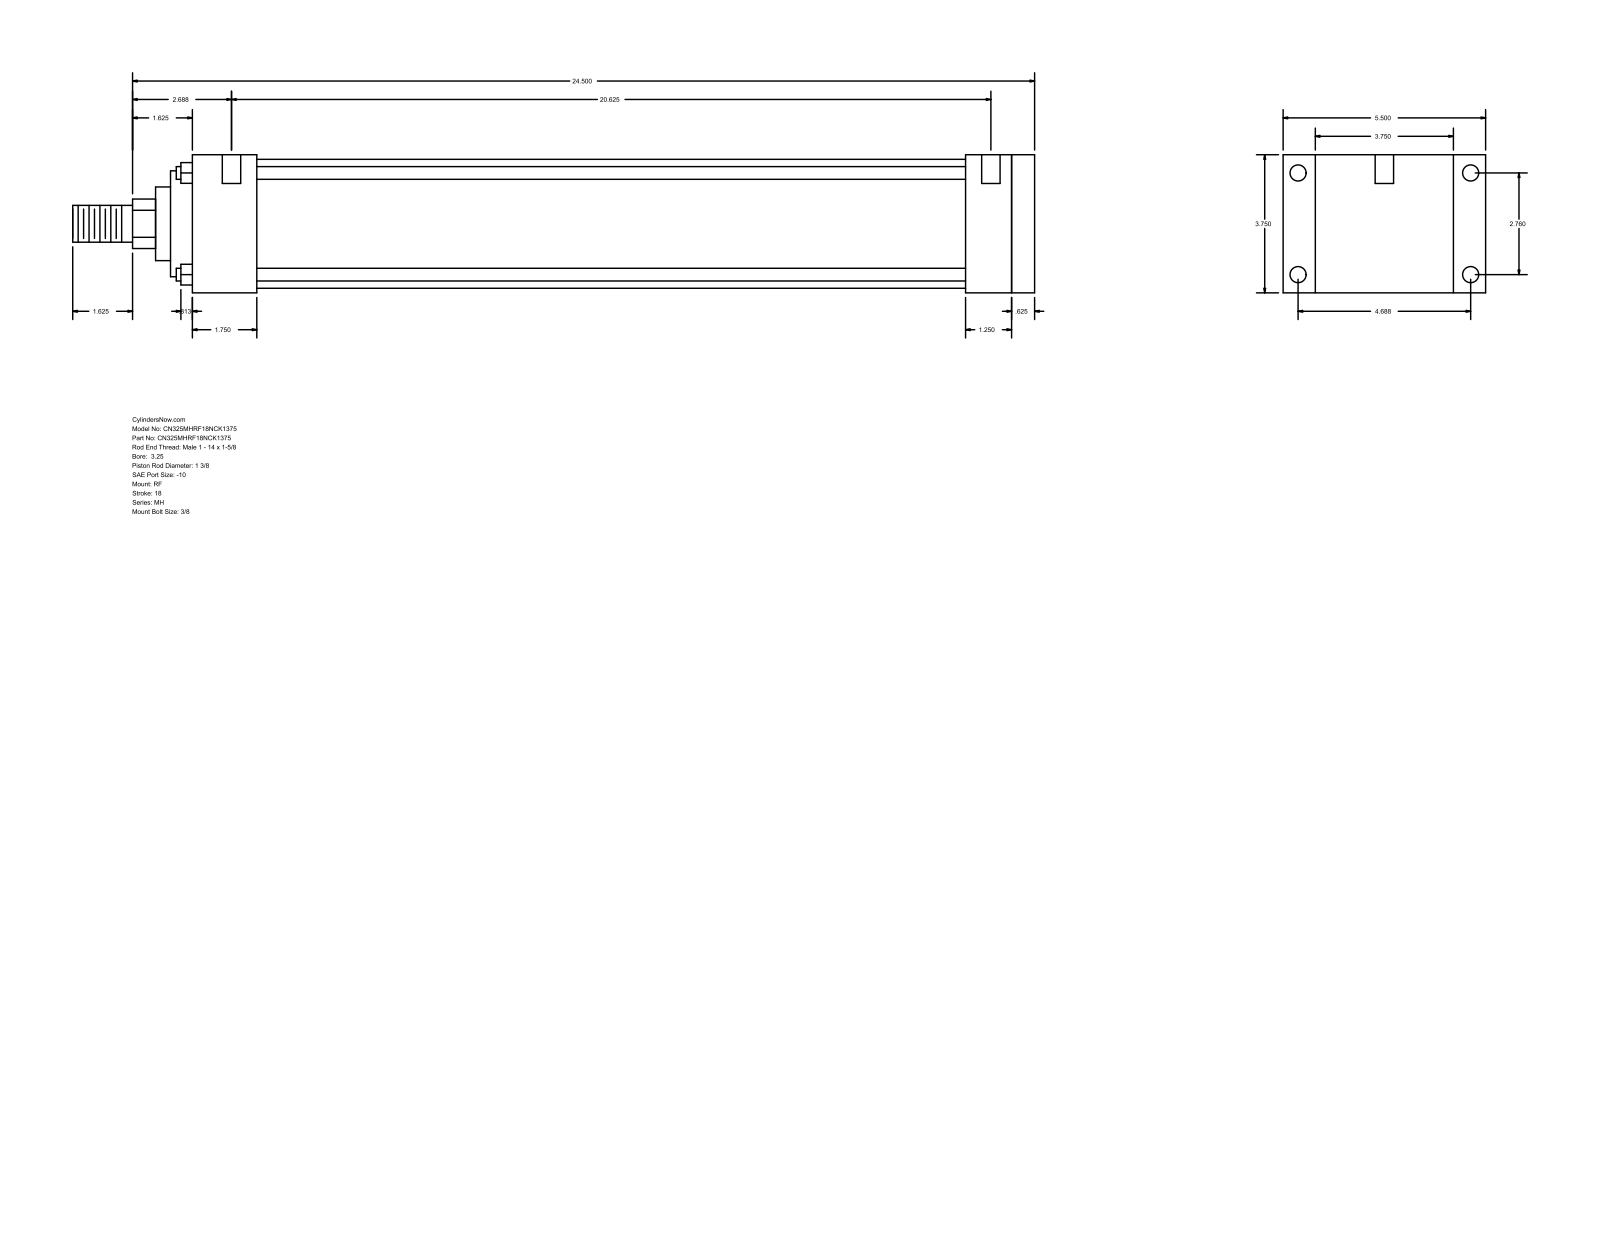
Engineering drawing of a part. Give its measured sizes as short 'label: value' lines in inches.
name: MH_RF__0325_1.375
written by: GSSL Pune (CONFIG_CONTROL_DESIGN)
unit: in
bodies: 0 solids, 94 faces (65 planar, 29 cylindrical, 0 other)
size: 26.125 × 5.5 × 3.75
holes: 4× ⌀0.219, 4× ⌀0.438, 2× ⌀0.5
bosses: 4× ⌀0.345, 1× ⌀3.5, 1× ⌀2.875, 1× ⌀2, 1× ⌀1.375, 1× ⌀1
rounds: 1× R0.672
face distances: 3.75, 22.875, 0.625, 22.25, 0.875, 4.625, 1.75, 20.5, 21.125, 21
hole spacings: 2.76, 4.687, 5.439, 20.875, 0.063, 0.187, 20.625, 20.688
